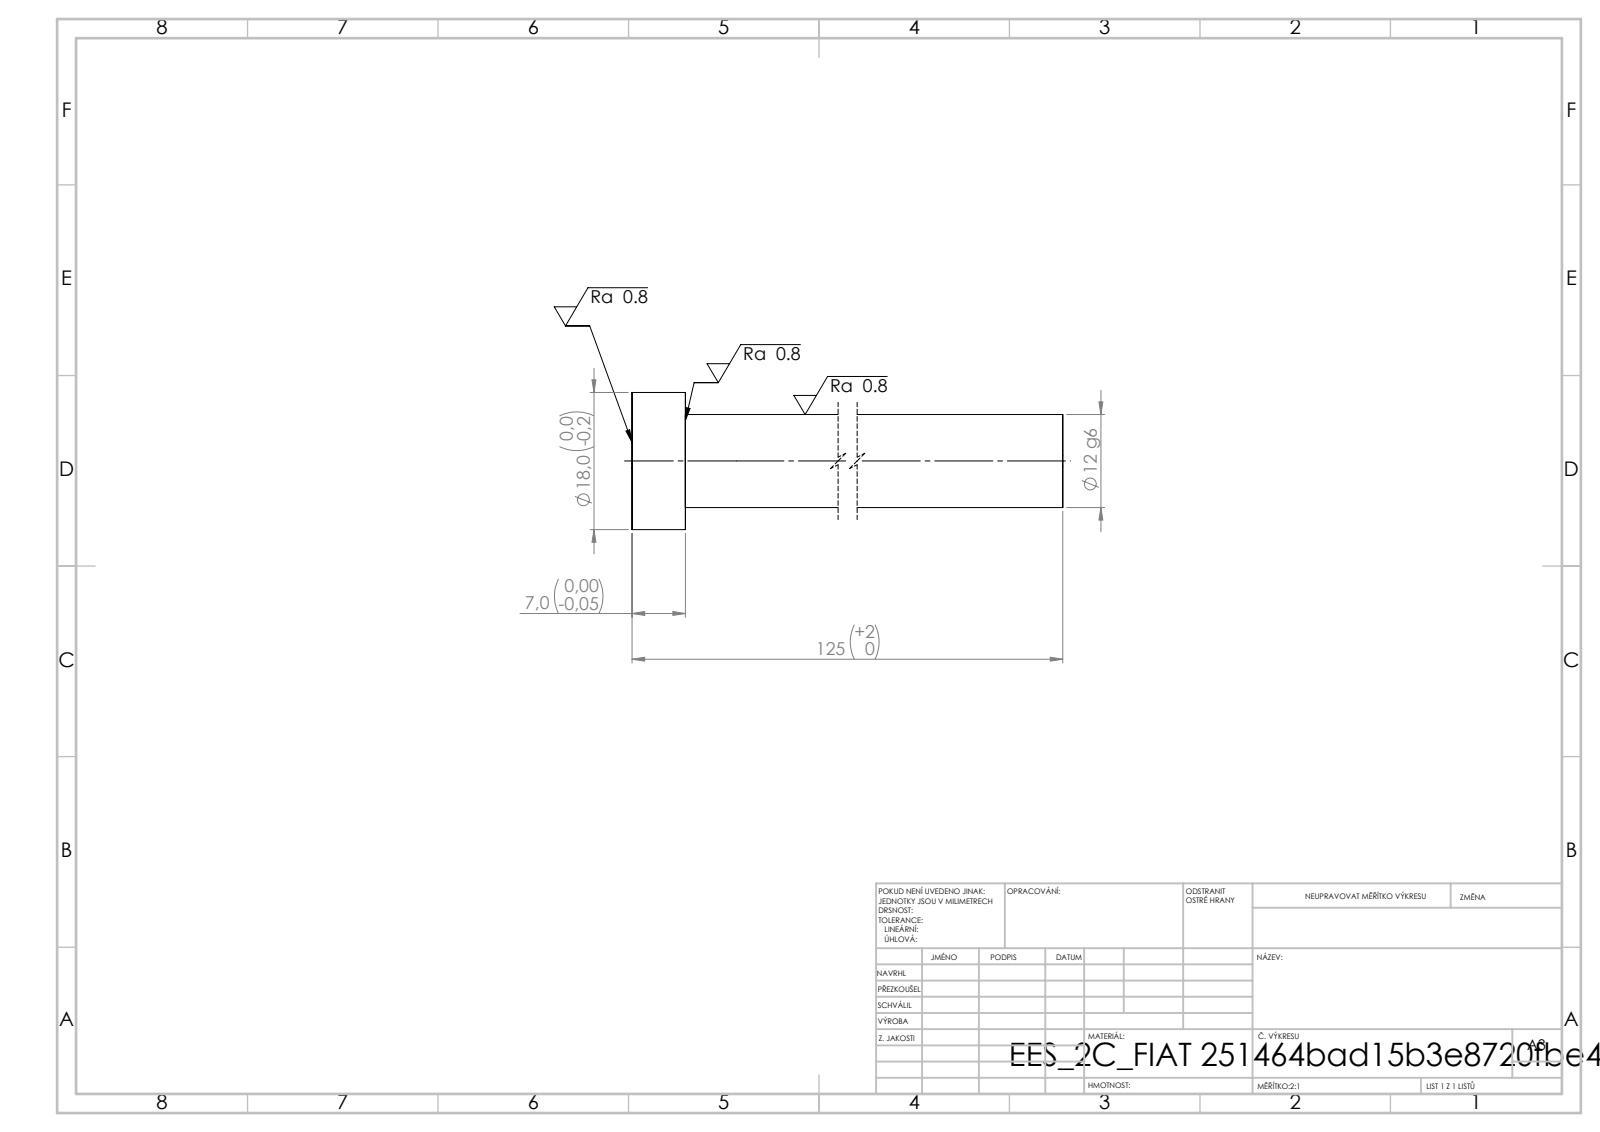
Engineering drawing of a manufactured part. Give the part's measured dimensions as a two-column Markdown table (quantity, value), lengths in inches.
| quantity | value |
| --- | --- |
| STEP written by | SolidWorks 2019 (CONFIG_CONTROL_DESIGN) |
| units | inches |
| bodies | 1 solid, 7 faces (3 planar, 4 cylindrical, 0 other) |
| overall size | 4.921 × 0.709 × 0.709 |
| volume | 0.95 in³ |
| surface area | 8.412 in² |
| round bosses / shafts (diameter × count) | 0.709 × 1, 0.48 × 1 |
| main face-to-face distances | 0.276, 4.921, 4.646 |
